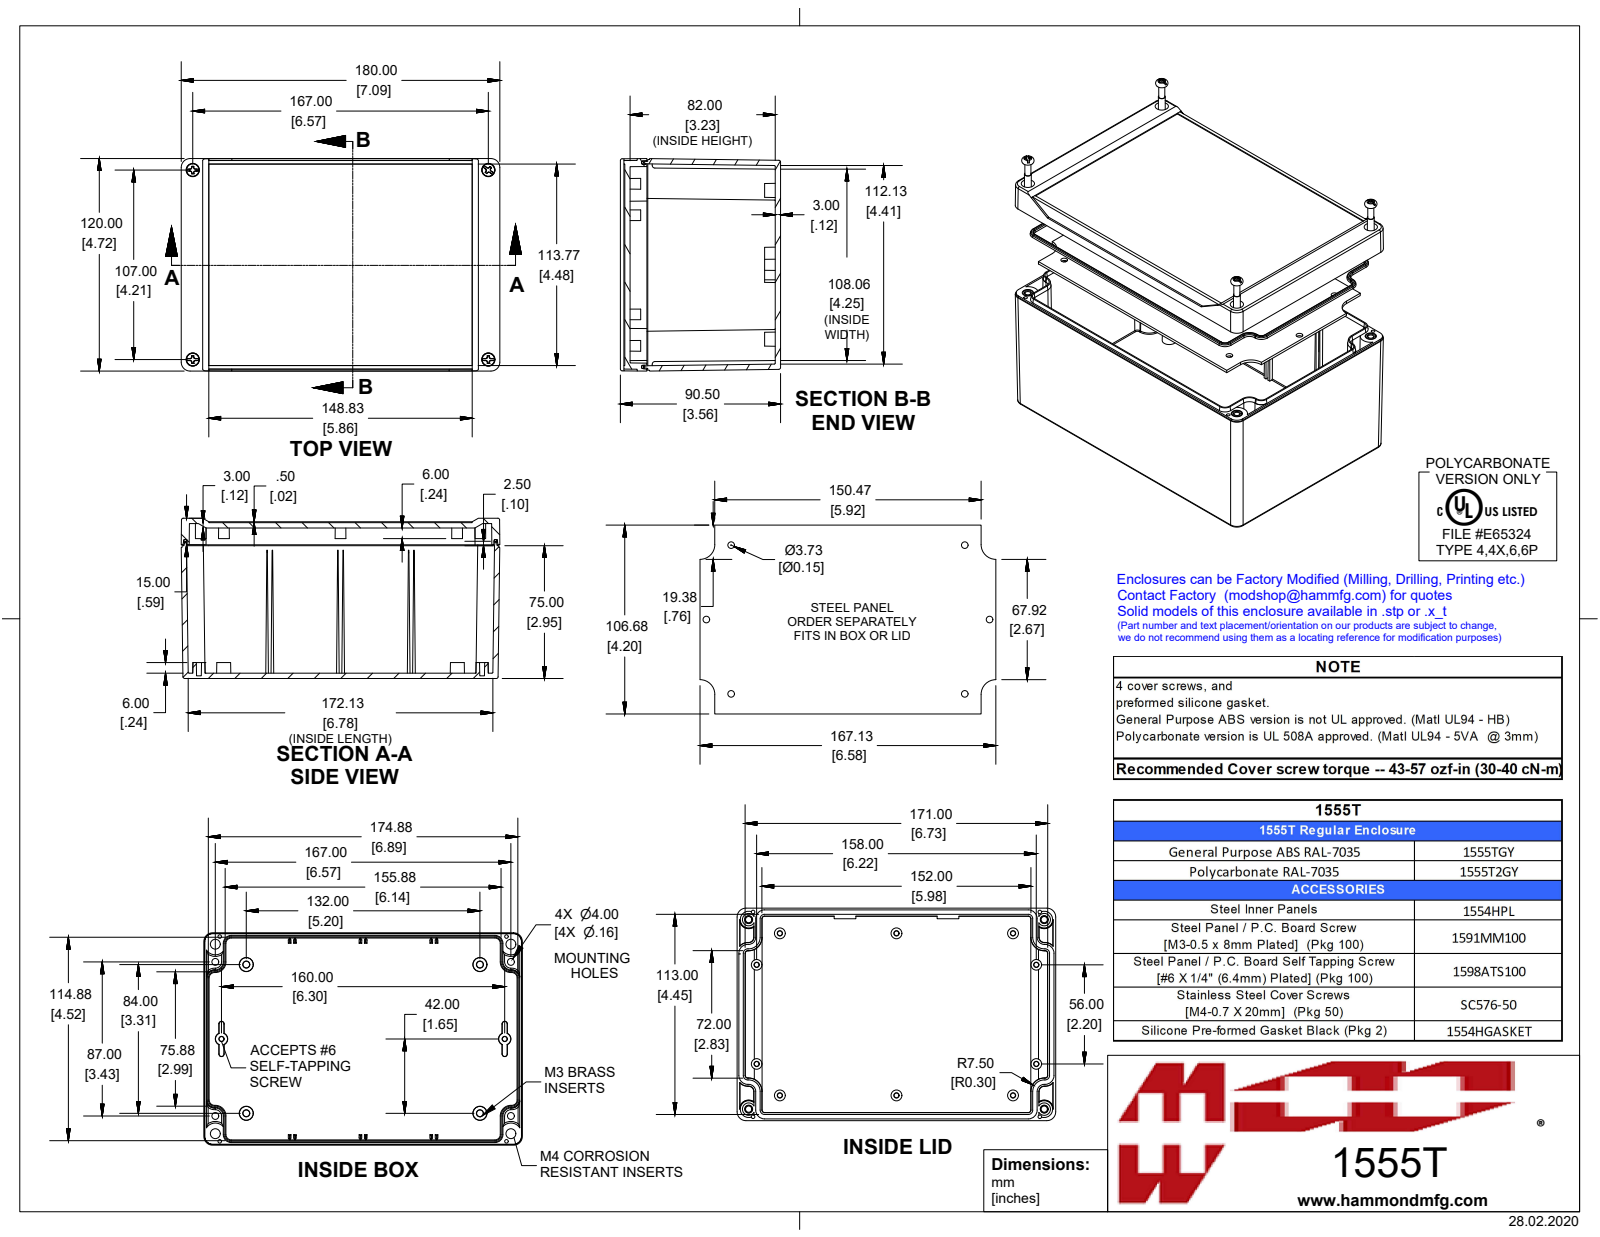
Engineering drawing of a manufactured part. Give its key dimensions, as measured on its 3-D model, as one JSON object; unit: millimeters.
{"part_name": "1555T2GY", "step_written_by": "SolidWorks 2019 (AUTOMOTIVE_DESIGN)", "units": "millimeters", "bodies": {"solids": 16, "faces": 1410, "planar": 430, "cylindrical": 346, "other": 634}, "overall_size": [180, 120, 90.5], "volume_mm3": 335800, "surface_area_mm2": 257800, "round_holes": [[2, 4], [2.5, 4], [3.3, 4], [3.5, 4], [3.7, 4], [7, 4], [2.8, 2]], "round_bosses_or_shafts": [[6.4, 4], [6, 4], [5.5, 4], [5.3, 4], [4.8, 4], [3.9, 4], [3.9, 4], [3.8, 4]], "partial_cylinders_radius": [[0.5, 32], [1, 8], [5, 8], [4.7, 4], [8.3, 4], [1.5, 2]], "face_to_face_distances": [3, 85, 9, 6, 10.6, 7.6, 1.6, 79, 88, 77.4], "hole_center_spacings": [5, 20.9, 21.8, 44.3, 53.6, 57.8, 97.1, 100.9]}
